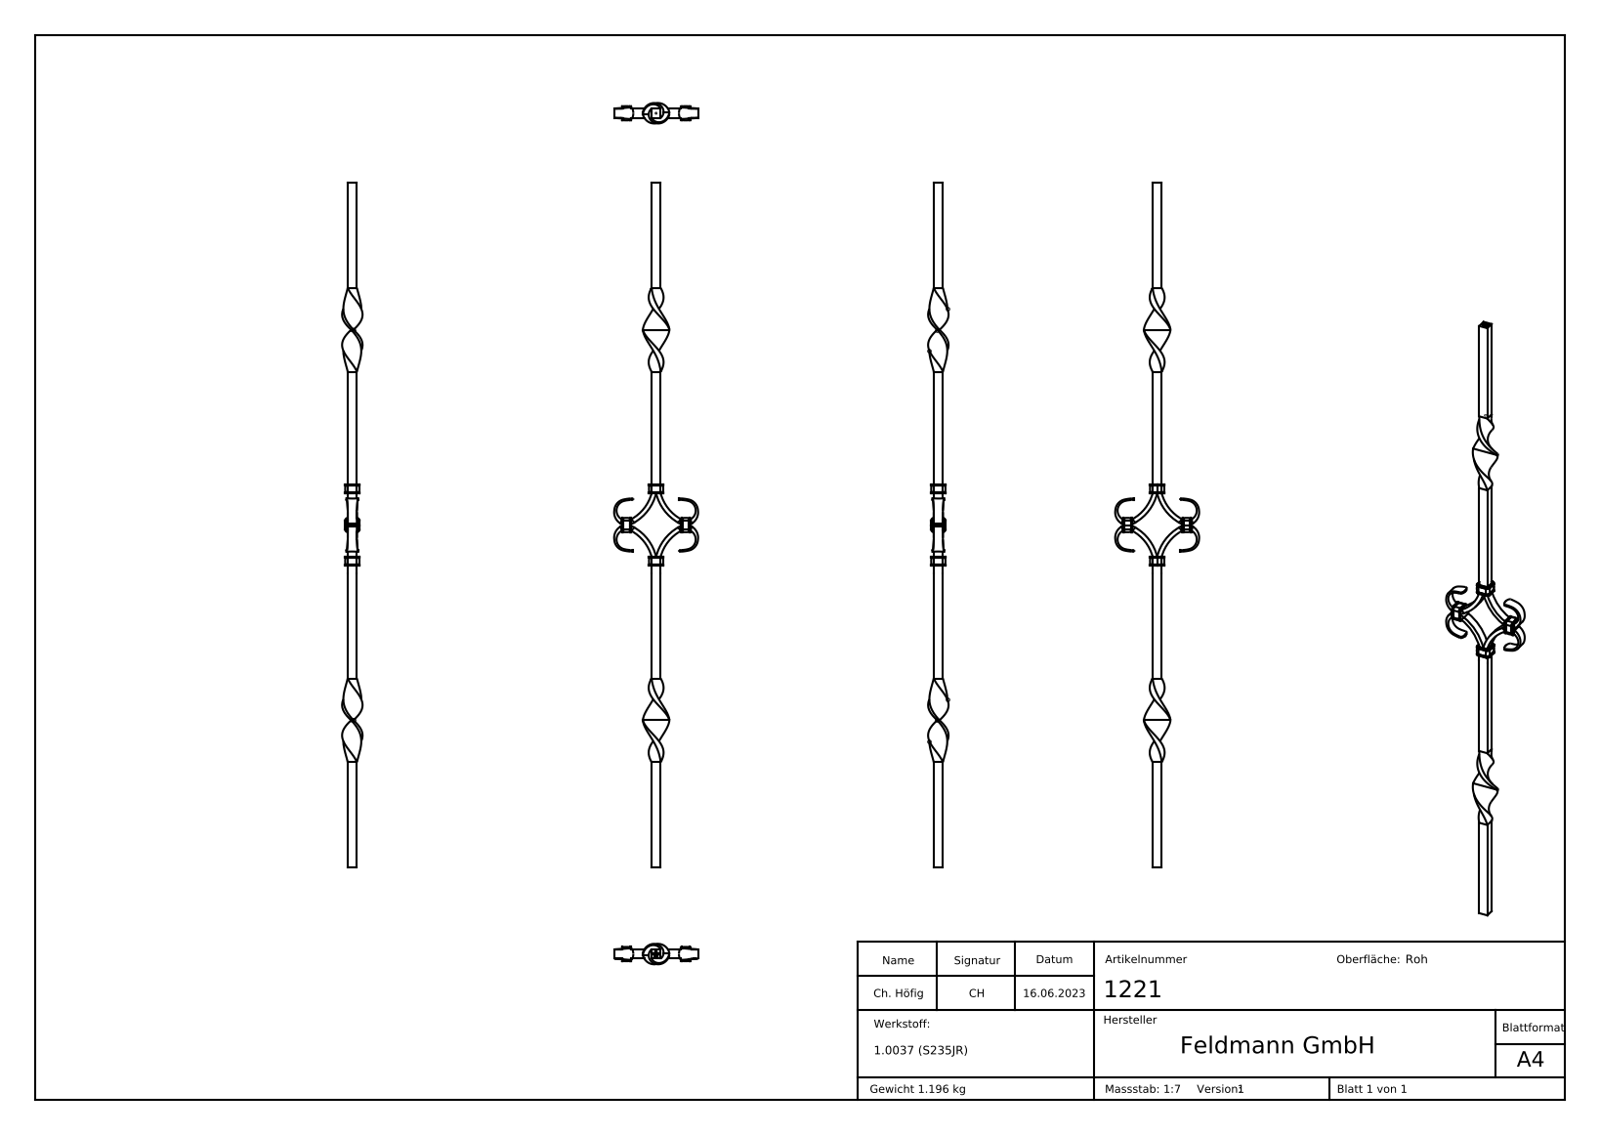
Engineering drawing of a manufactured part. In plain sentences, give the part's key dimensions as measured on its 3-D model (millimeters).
The part is named "1221". Its 3-D file was written by "SolidWorks 2018 (CONFIG_CONTROL_DESIGN)". It is 3 solids with 860 faces: 352 planar, 244 cylindrical and 264 other. Overall it measures 900 by 110.31 by 26.84 millimeters. Its volume is 153 336 cubic millimeters and its surface area 65 454 square millimeters. Partial cylindrical surfaces (rounded edges, fillets, slot ends): 88 of radius 0.5, 32 of radius 0.2, 16 of radius 10.62, 8 of radius 1, 8 of radius 4, 4 of radius 13, 4 of radius 18.81, 4 of radius 55. The main face-to-face distances are 12, 0.5, 12.5, 13, 39, 443.5, 456.5, 95, 51, 408.5.
